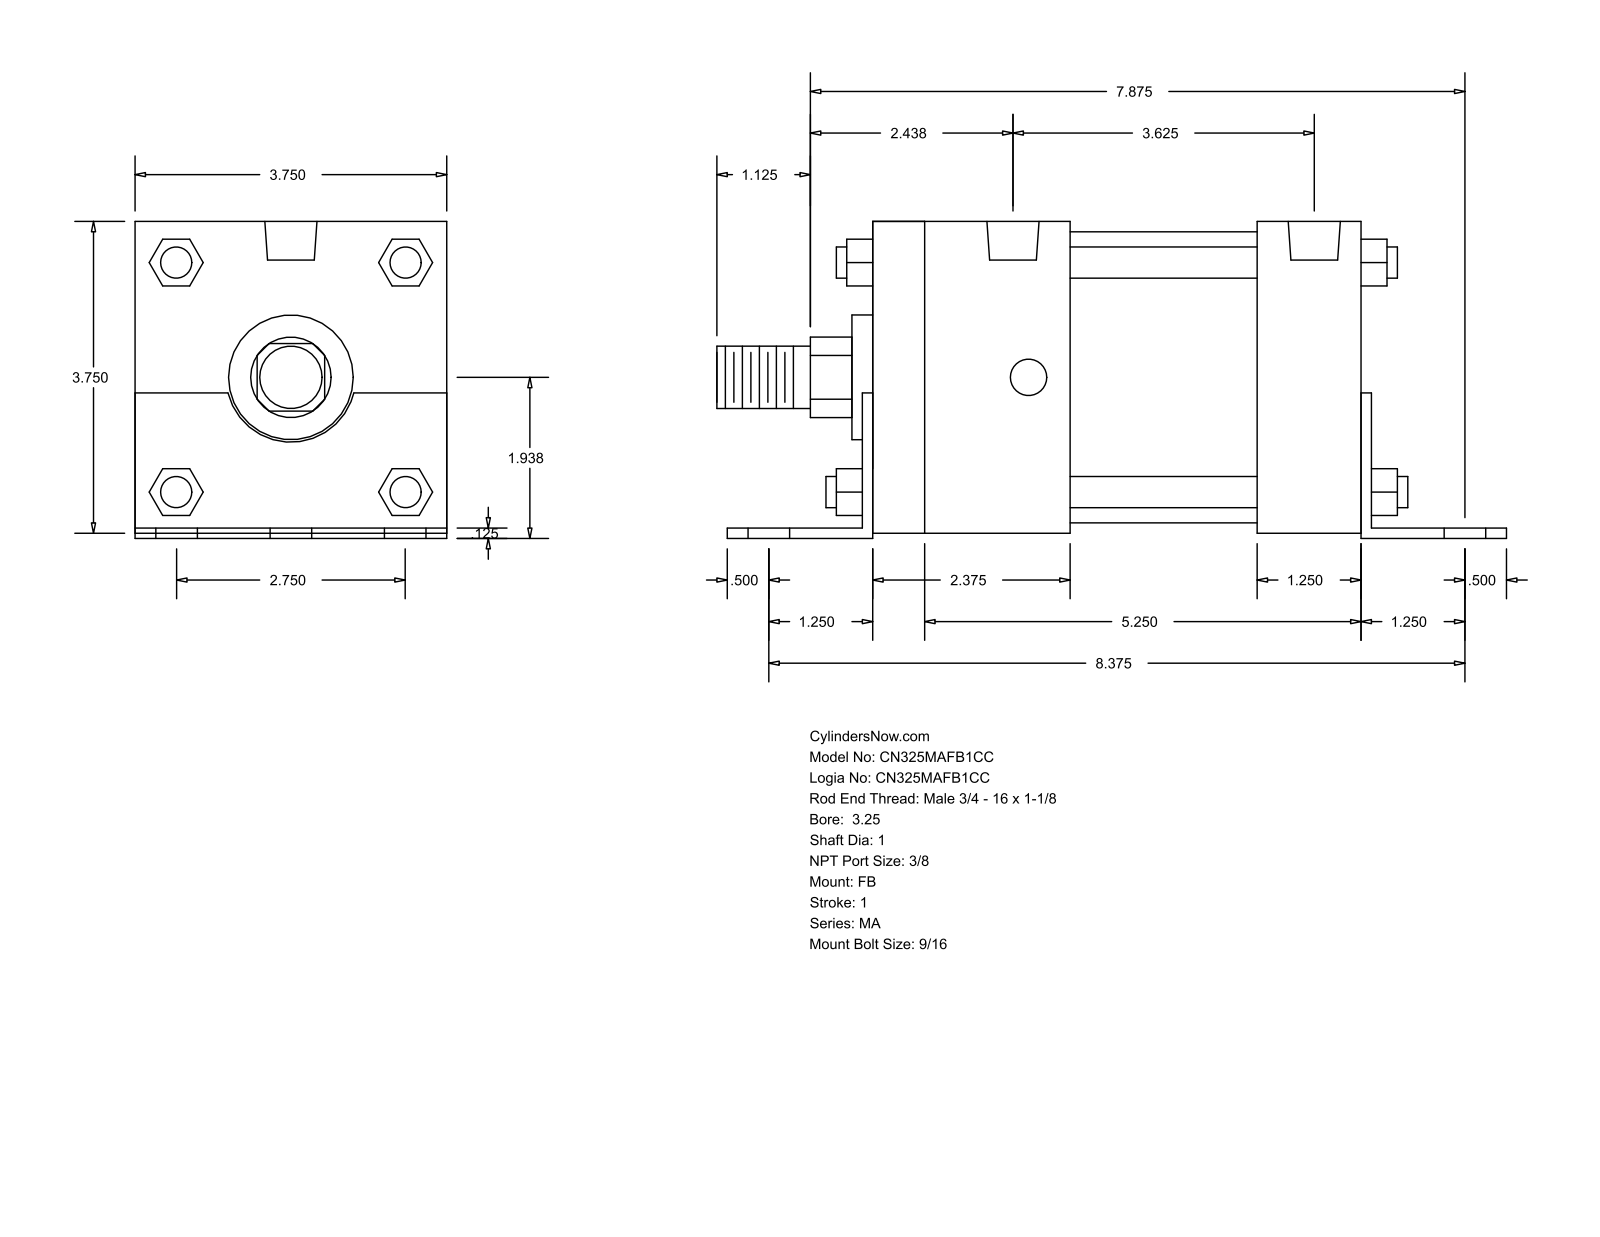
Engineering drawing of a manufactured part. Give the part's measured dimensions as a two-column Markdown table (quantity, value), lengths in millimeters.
| quantity | value |
| --- | --- |
| part name | MA_FB__0325_1 |
| STEP written by | GSSL Pune (CONFIG_CONTROL_DESIGN) |
| units | millimeters |
| bodies | 0 solids, 140 faces (105 planar, 35 cylindrical, 0 other) |
| overall size | 241.3 × 96.84 × 95.25 |
| round holes (diameter × count) | 14.29 × 6, 11.11 × 4, 15.93 × 2 |
| round bosses / shafts (diameter × count) | 9.53 × 4, 88.9 × 1, 38.1 × 1, 25.4 × 1, 19.05 × 1 |
| partial cylindrical surfaces (radius × count) | 12.29 × 1, 19.81 × 1 |
| main face-to-face distances | 95.24, 3.17, 1.59, 96.83, 1.58, 93.66, 152.4, 149.23, 155.57, 120.65 |
| hole center spacings | 34.92, 215.58, 212.73, 57.78, 61.65, 69.84, 82.38, 82.55 |
